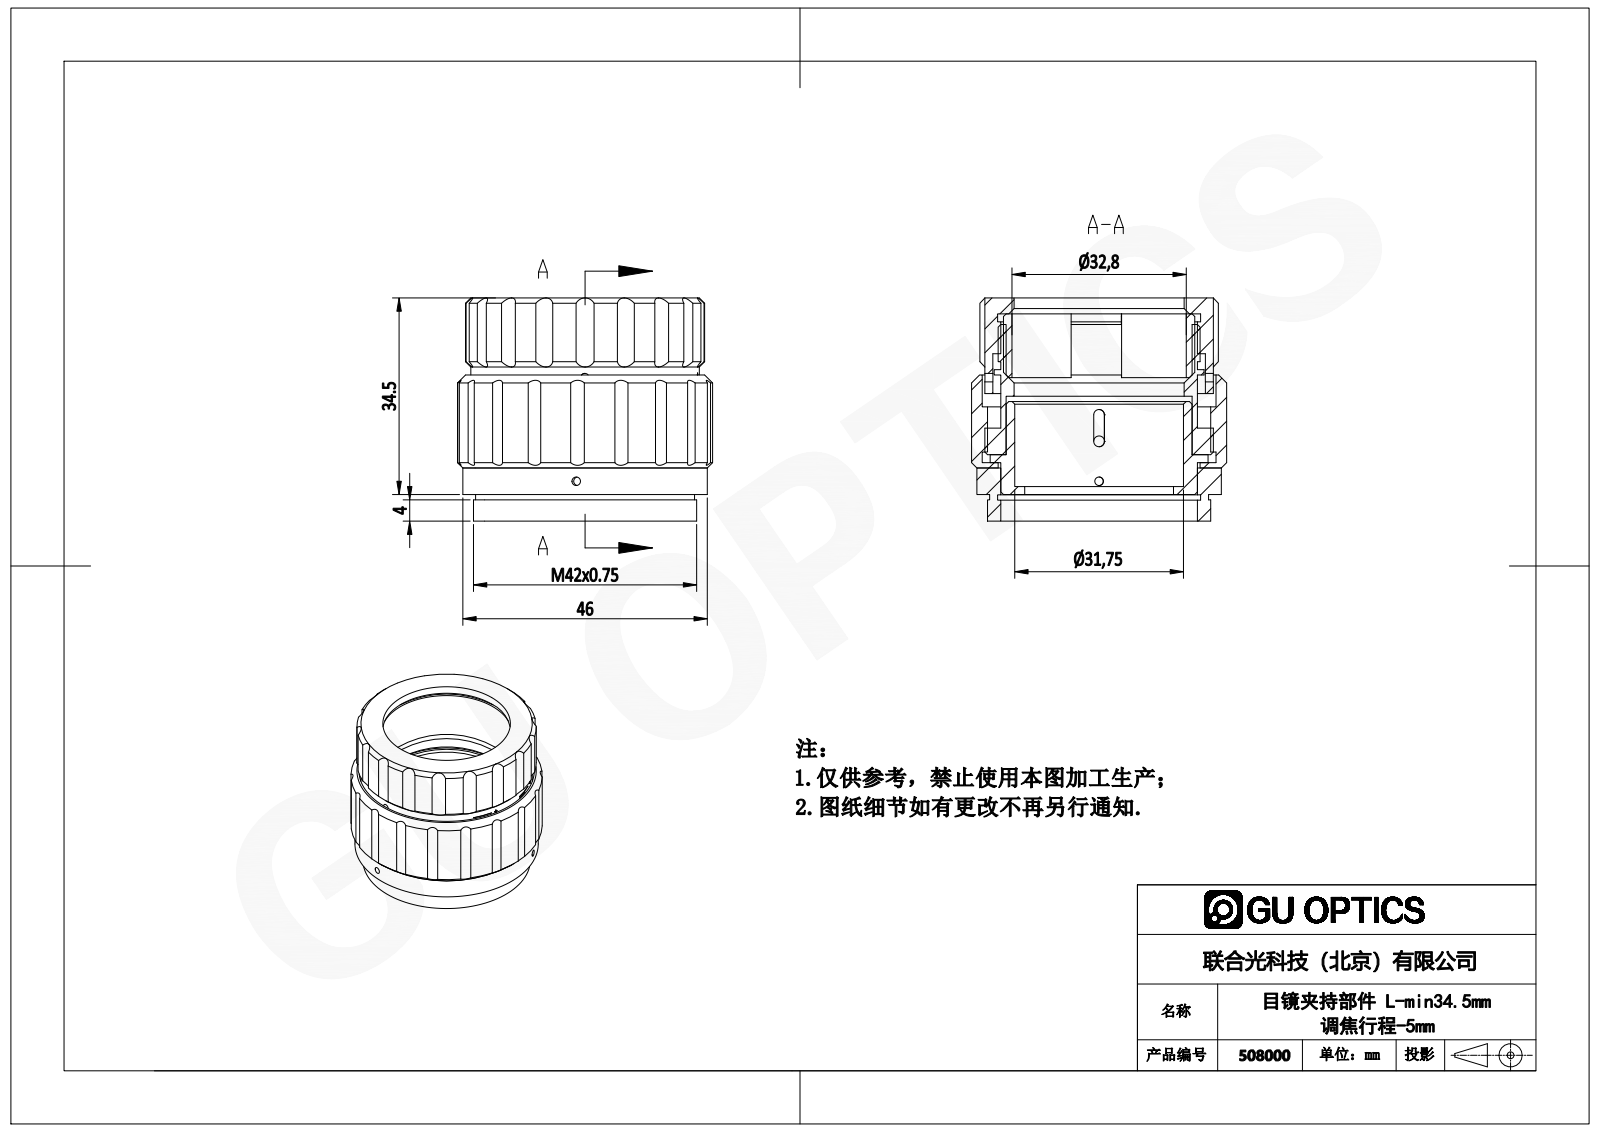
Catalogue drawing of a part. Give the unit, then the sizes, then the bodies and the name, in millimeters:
Units: millimetres
Overall size (bounding box): 48 × 48 × 42
Round holes (diameter × count): ⌀1.6 ×7, ⌀2.05 ×1, ⌀28 ×1, ⌀31.75 ×1, ⌀32 ×1, ⌀32.8 ×1, ⌀35 ×1, ⌀37 ×1, ⌀38 ×1, ⌀38.2 ×1, ⌀40 ×1, ⌀42 ×1
Round bosses / shafts (diameter × count): ⌀46 ×1, ⌀43 ×1, ⌀41.2 ×1, ⌀41 ×1, ⌀39.5 ×1, ⌀36 ×1
Partial cylindrical surfaces — rounded edges, fillets, slot ends (radius × count): R2 ×36, R1 ×2, R22.5 ×1, R24 ×1
Main face-to-face distances: 5, 7.5, 6, 17.5, 11, 2.5, 6.5, 1.5, 1, 12.5
Volume: 29 533 mm³ · Surface area: 31 586 mm²
Bodies: 6 solids, 273 faces (36 planar, 180 cylindrical, 57 other)
Part name (STEP PRODUCT): 508000
STEP written by: SolidWorks 2020 (CONFIG_CONTROL_DESIGN)
